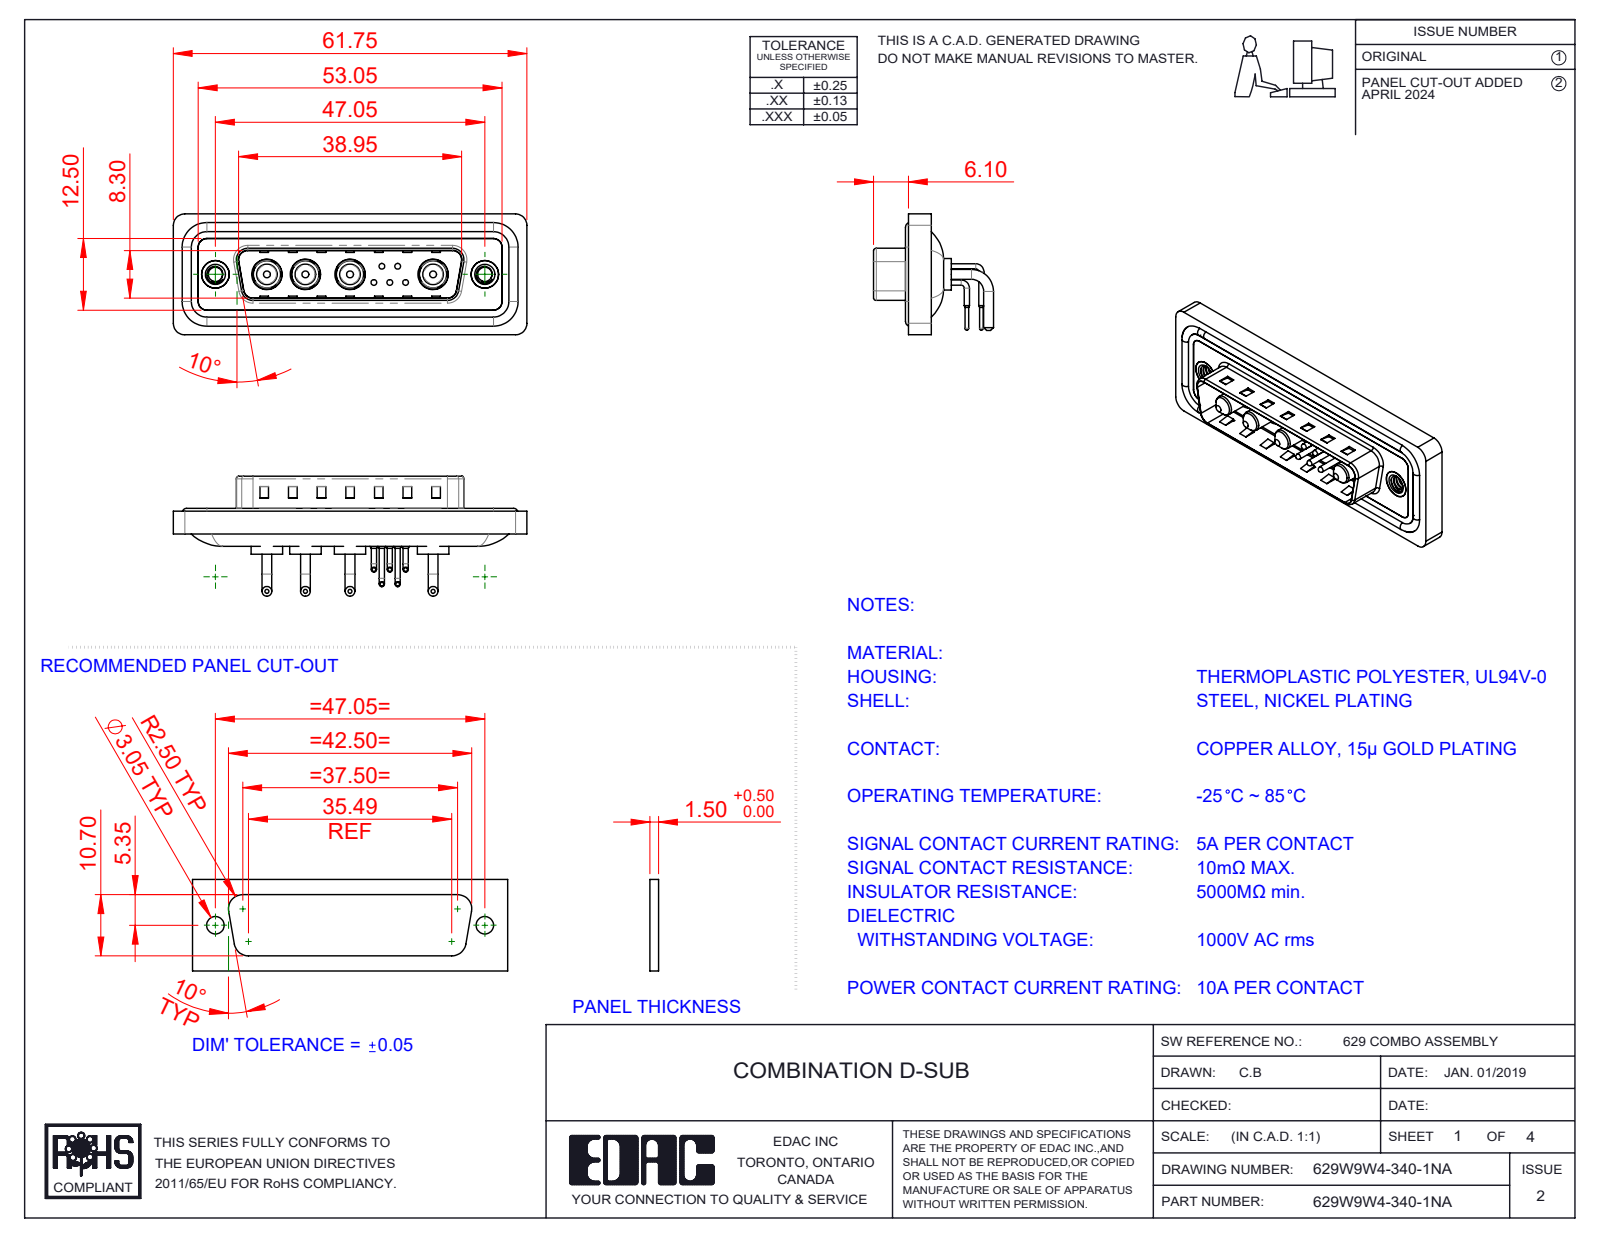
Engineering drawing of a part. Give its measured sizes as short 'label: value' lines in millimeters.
name: 629Combo Contact Row 1; 629W9W4-340-1NA; Power Pin_10A RA; 629Combo Contact Row 2 (+5 more)
written by: SolidWorks 2023 (CONFIG_CONTROL_DESIGN)
unit: mm
bodies: 20 solids, 1199 faces (569 planar, 450 cylindrical, 180 other)
size: 61.75 × 21.1 × 20.95
volume: 7 476 mm³; area: 12 176 mm²
holes: 5× ⌀0.75, 5× ⌀1.6, 5× ⌀2, 4× ⌀4.85, 4× ⌀5.3, 2× ⌀2.5, 2× ⌀4, 2× ⌀4.8, 2× ⌀5
bosses: 10× ⌀0.9, 8× ⌀1.7, 5× ⌀1.5, 5× ⌀1, 5× ⌀0.65, 4× ⌀5.5, 4× ⌀5.2, 4× ⌀4.75
rounds: 18× R1.5, 18× R2, 8× R0.5, 8× R1.6, 5× R1.01, 4× R0.25, 4× R0.6, 4× R0.65
face distances: 0.4, 2.9, 0.8, 4.1, 1.1, 4.5, 2.1, 1.5, 1.6, 3.1
hole spacings: 3.16, 2.77, 5.04, 14.5, 2.78, 4.4, 4.41, 5
